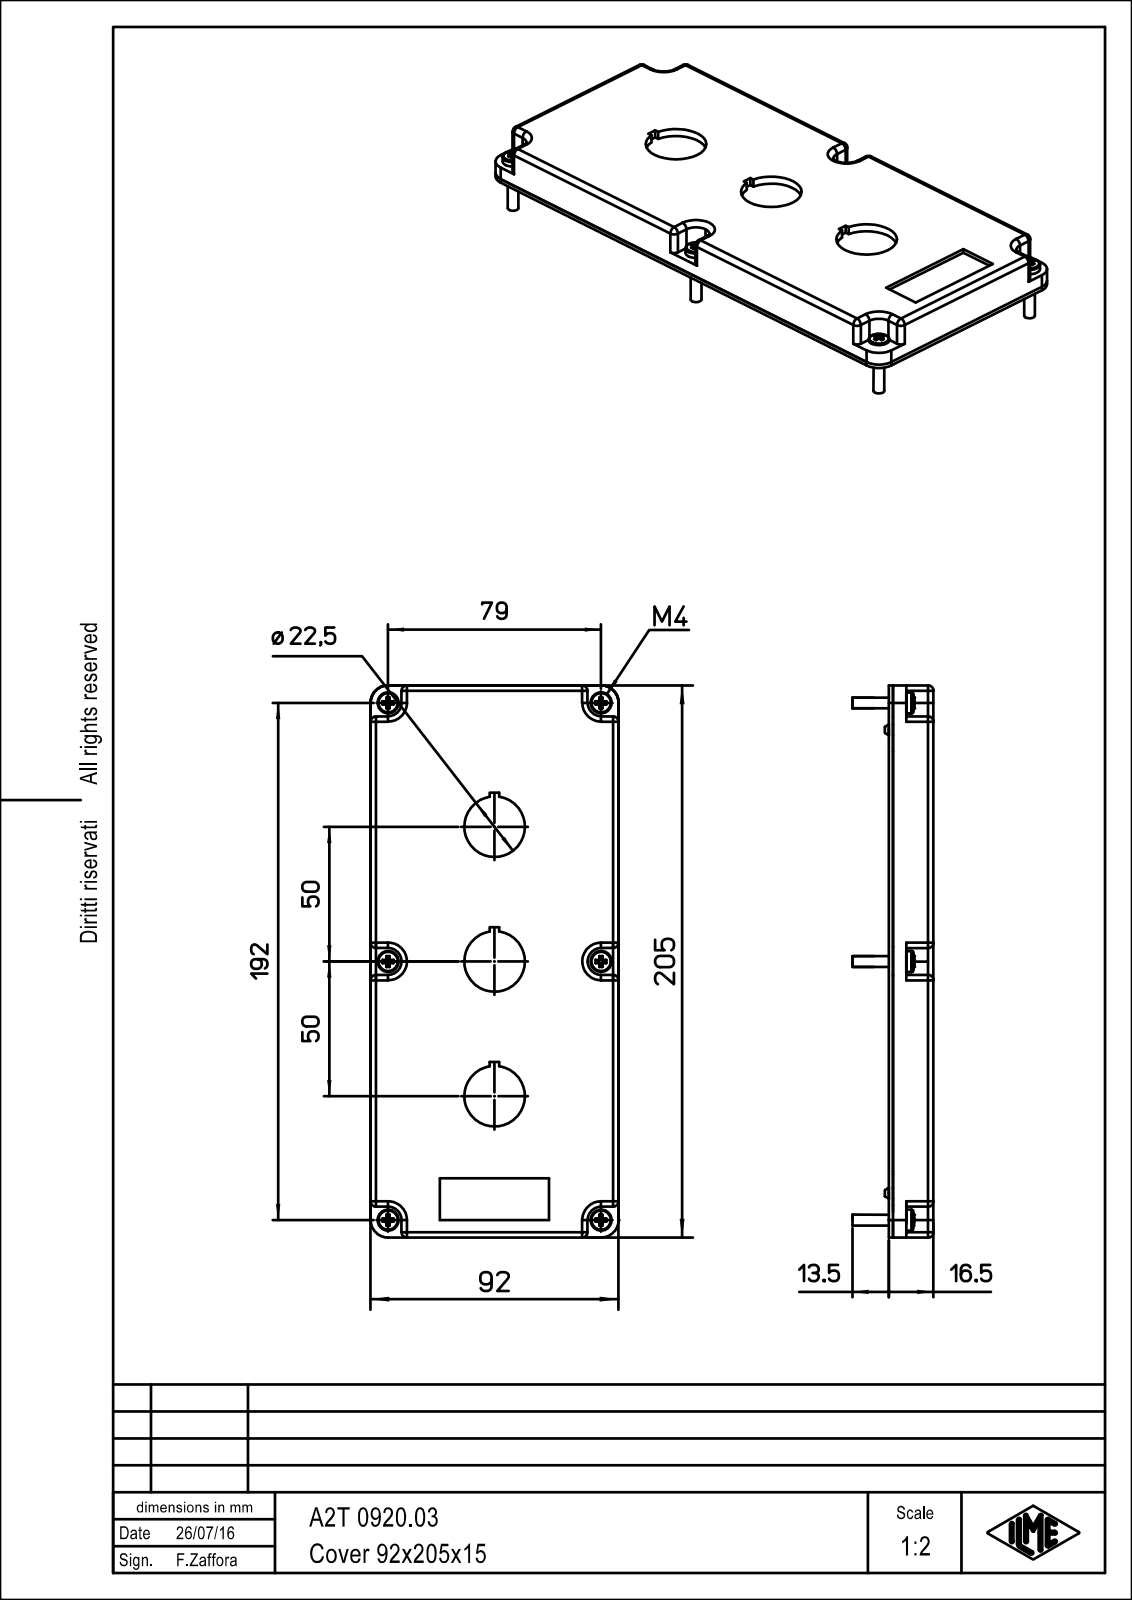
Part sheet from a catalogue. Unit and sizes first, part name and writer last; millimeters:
Units: millimetres
Overall size (bounding box): 205 × 92.02 × 30.01
Round holes (diameter × count): ⌀4.5 ×6, ⌀22.5 ×3, ⌀3.3 ×1, ⌀5.8 ×1
Round bosses / shafts (diameter × count): ⌀7.8 ×6, ⌀4 ×6, ⌀6 ×2, ⌀7 ×1, ⌀6.2 ×1
Partial cylindrical surfaces — rounded edges, fillets, slot ends (radius × count): R2 ×23, R0.33 ×11, R5 ×8, R6.5 ×8, R8 ×8, R0.27 ×2, R0.27 ×2, R0.5 ×2
Main face-to-face distances: 3, 13.5, 16.5, 1.5, 15, 12, 89, 92, 86, 202
Hole centre spacings: 60.63, 63.72, 96, 103.81, 124.33, 151.25, 79, 39.5
Volume: 89 634 mm³ · Surface area: 64 560 mm²
Bodies: 1 solid, 678 faces (485 planar, 143 cylindrical, 50 other)
Part name (STEP PRODUCT): A2T_0920.03
STEP written by: PTC Creo Elements/Direct Modeling 19.0B 21-Mar-2015 (C) Parametric Technology GmbH (AUTOMOTIVE_DESIGN)
